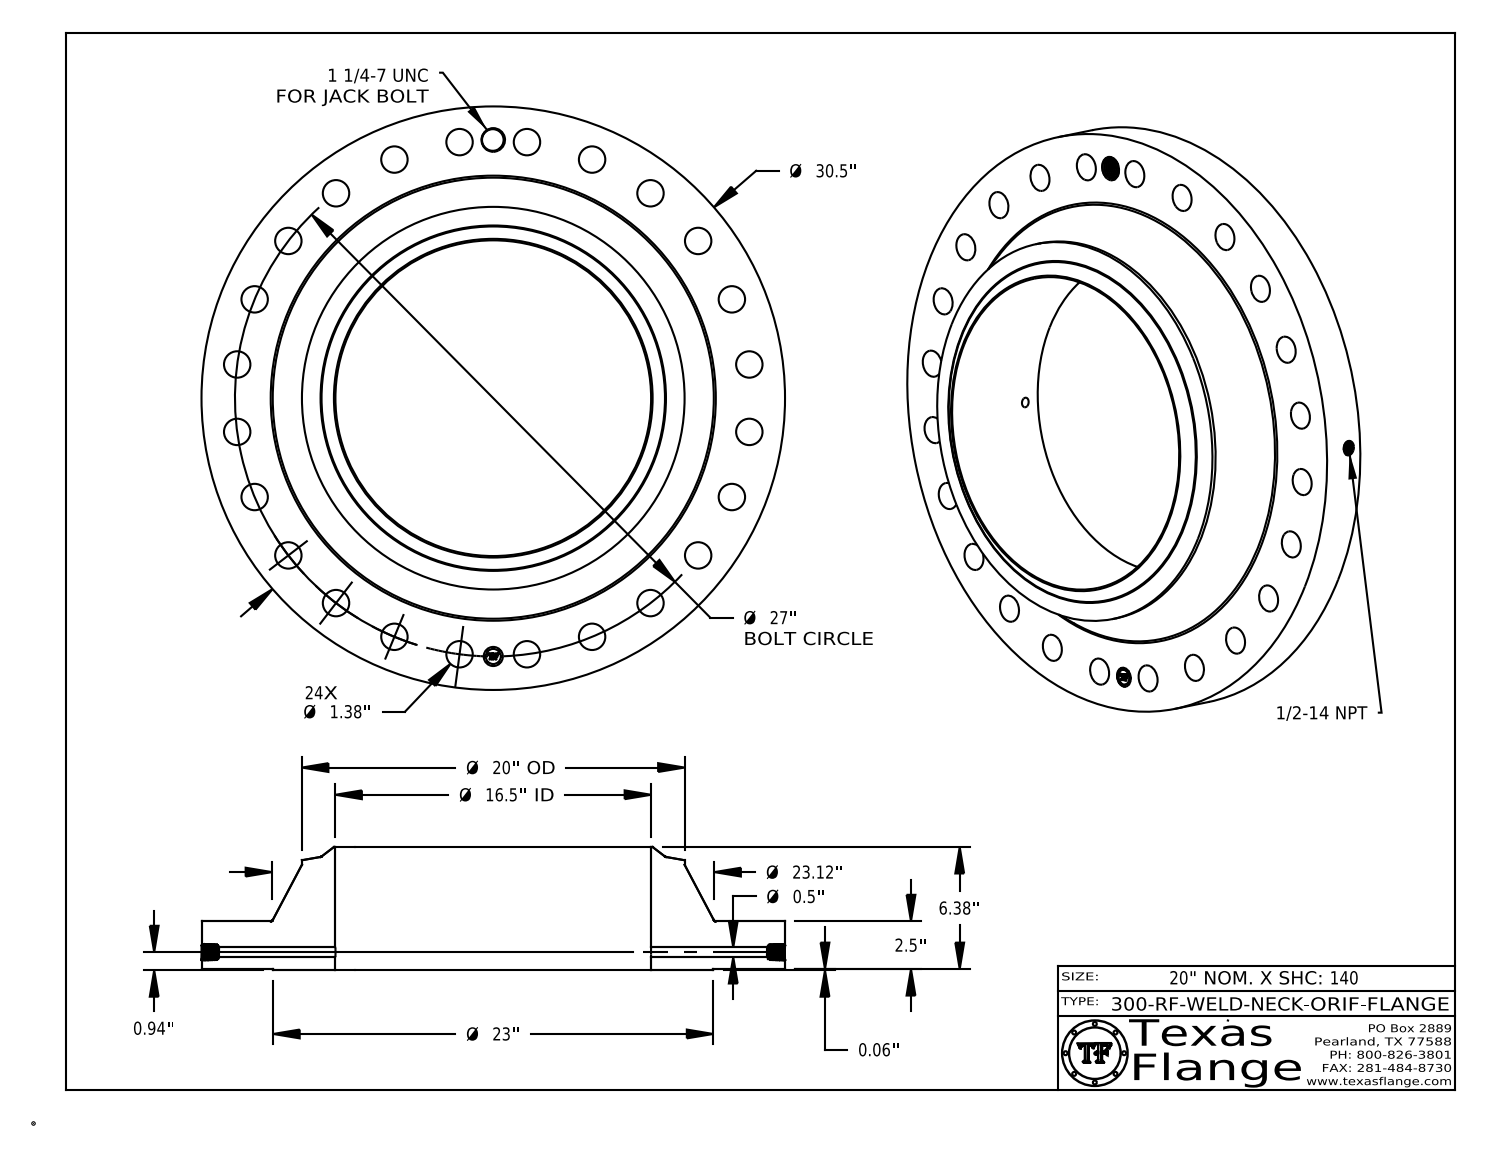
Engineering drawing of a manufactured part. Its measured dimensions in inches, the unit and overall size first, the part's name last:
Units: inches
Overall size (bounding box): 30.5 × 30.5 × 6.44
Round holes (diameter × count): ⌀1.38 ×24, ⌀0.5 ×1, ⌀0.672 ×1, ⌀1 ×1, ⌀1.109 ×1, ⌀16.5 ×1
Round bosses / shafts (diameter × count): ⌀0.061 ×8, ⌀30.5 ×1, ⌀23 ×1, ⌀20 ×1, ⌀0.788 ×1
Main face-to-face distances: 2.5, 0.06, 2.56, 6.44, 6.38, 3.88, 2.545, 2.485, 0.015, 3.895
Hole centre spacings: 13.5, 23.383, 24.945, 21.42, 3.524, 6.988, 19.092, 26.08
Volume: 1 705 in³ · Surface area: 1 981 in²
Bodies: 1 solid, 822 faces (369 planar, 131 cylindrical, 322 other)
Part name (STEP PRODUCT): 300-RF-WELD-NECK
STEP written by: CATIA V5 STEP AP214 (AUTOMOTIVE_DESIGN)
